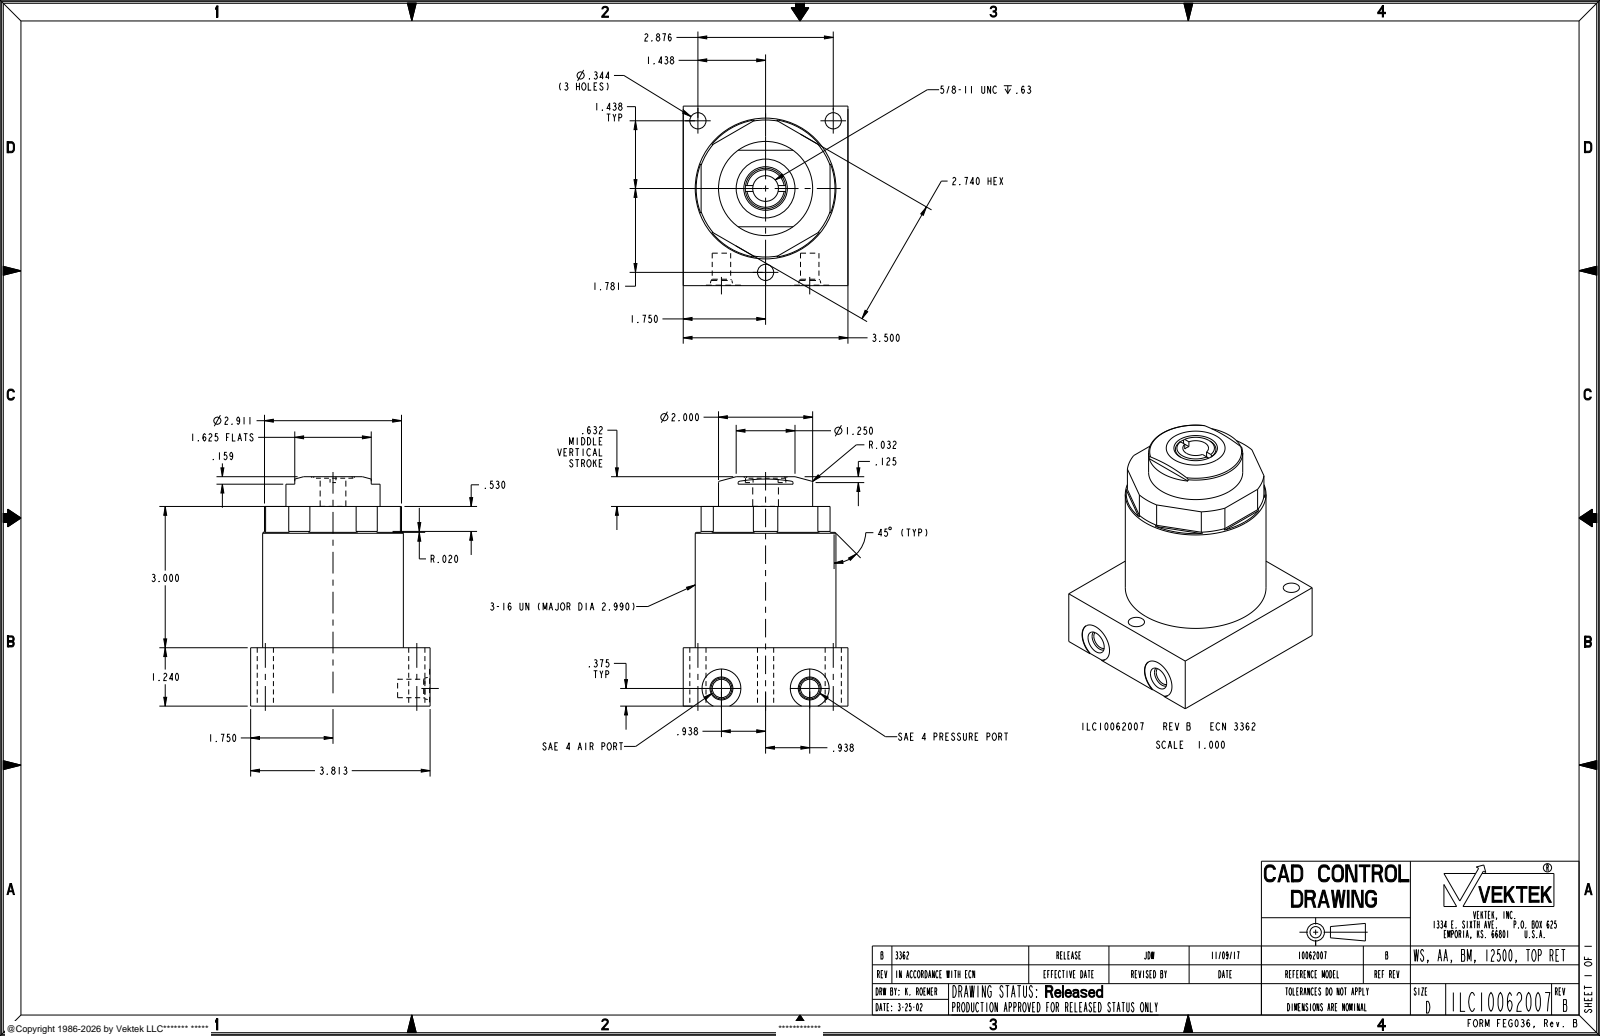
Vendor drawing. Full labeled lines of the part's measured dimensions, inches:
Part name (STEP PRODUCT): ILC10062007
STEP written by: PRO/ENGINEER BY PARAMETRIC TECHNOLOGY CORPORATION, 2013320 (AUTOMOTIVE_DESIGN)
Units: inches
Bodies: 1 solid, 87 faces (37 planar, 32 cylindrical, 18 other)
Overall size (bounding box): 4.872 × 3.813 × 3.5
Volume: 38.4 in³ · Surface area: 82.4 in²
Round holes (diameter × count): ⌀0.344 ×3, ⌀0.392 ×2, ⌀0.825 ×2, ⌀0.546 ×1
Round bosses / shafts (diameter × count): ⌀2.99 ×1, ⌀2 ×1
Partial cylindrical surfaces — rounded edges, fillets, slot ends (radius × count): R0.02 ×6, R0.431 ×1, R1.456 ×1
Main face-to-face distances: 1.24, 3.5, 3.813, 4.24, 3, 2.74, 0.38, 3.12, 4.872, 3.632
Hole centre spacings: 2.034, 3.526, 1.781, 1.876, 2.876
